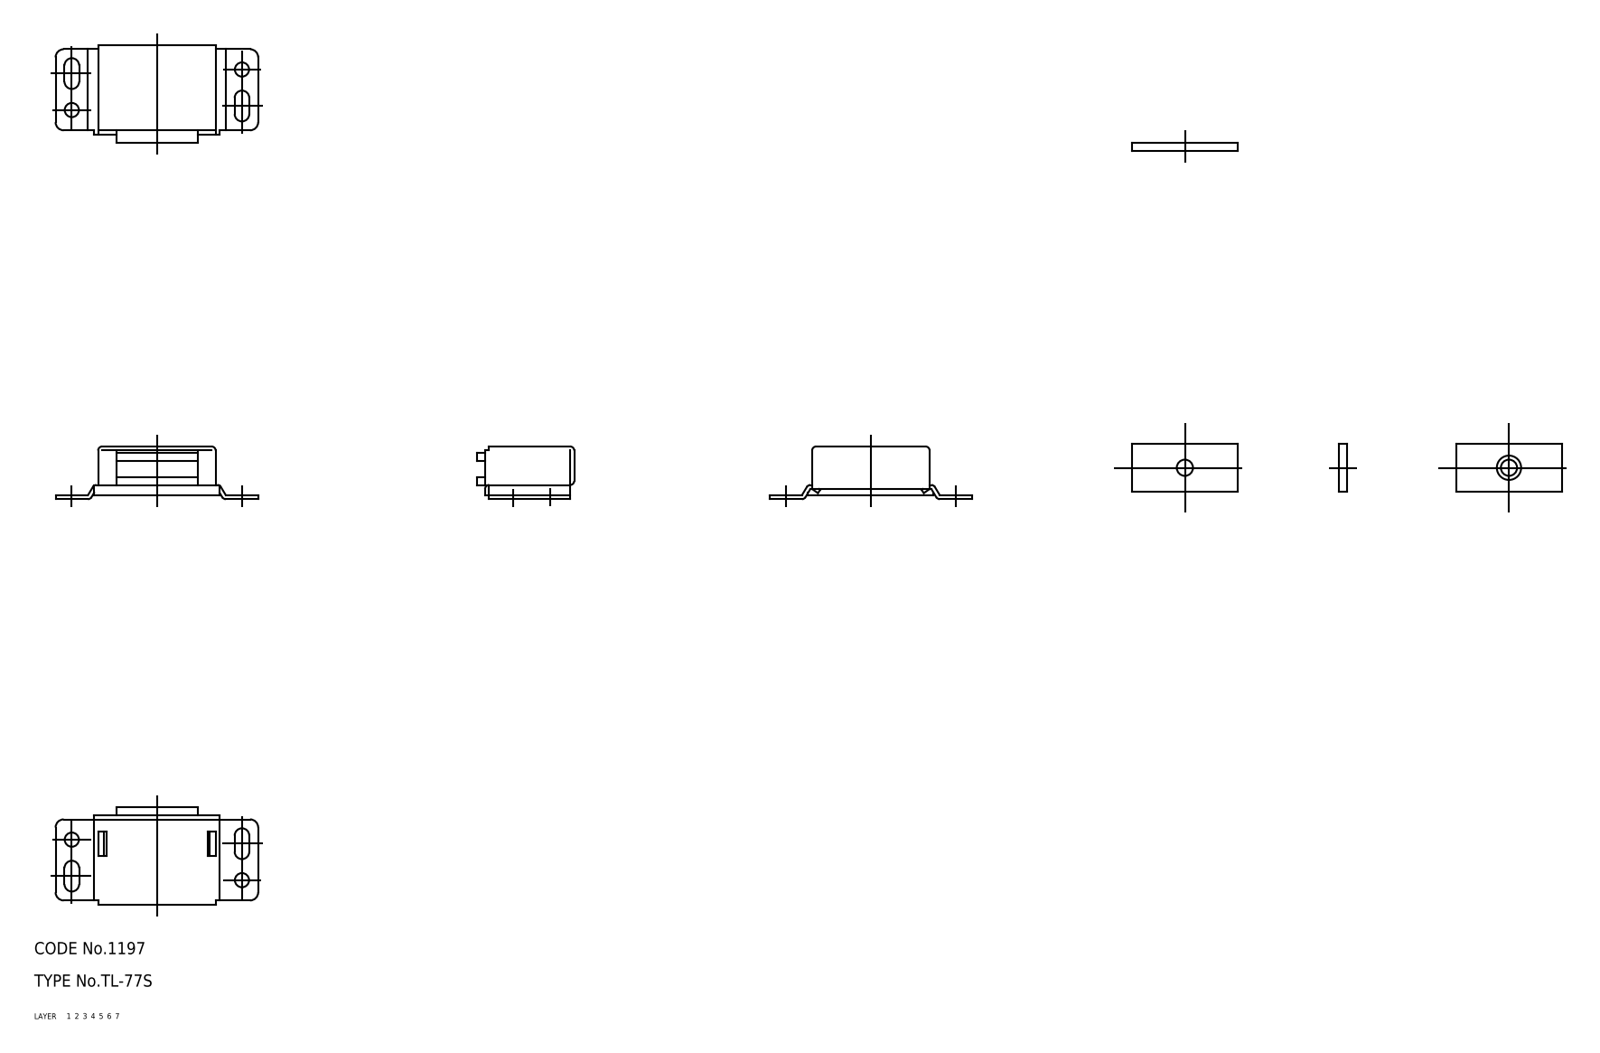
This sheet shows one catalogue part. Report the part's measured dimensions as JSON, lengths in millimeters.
{"part_name": "67113279; 67113292; 67113305; 67113318 (+1 more)", "step_written_by": "CADfix (AUTOMOTIVE_DESIGN)", "units": "millimeters", "bodies": {"solids": 5, "faces": 121, "planar": 0, "cylindrical": 0, "other": 121}, "overall_size": [50, 40.27, 13.75], "volume_mm3": 5815, "surface_area_mm2": 8897}
